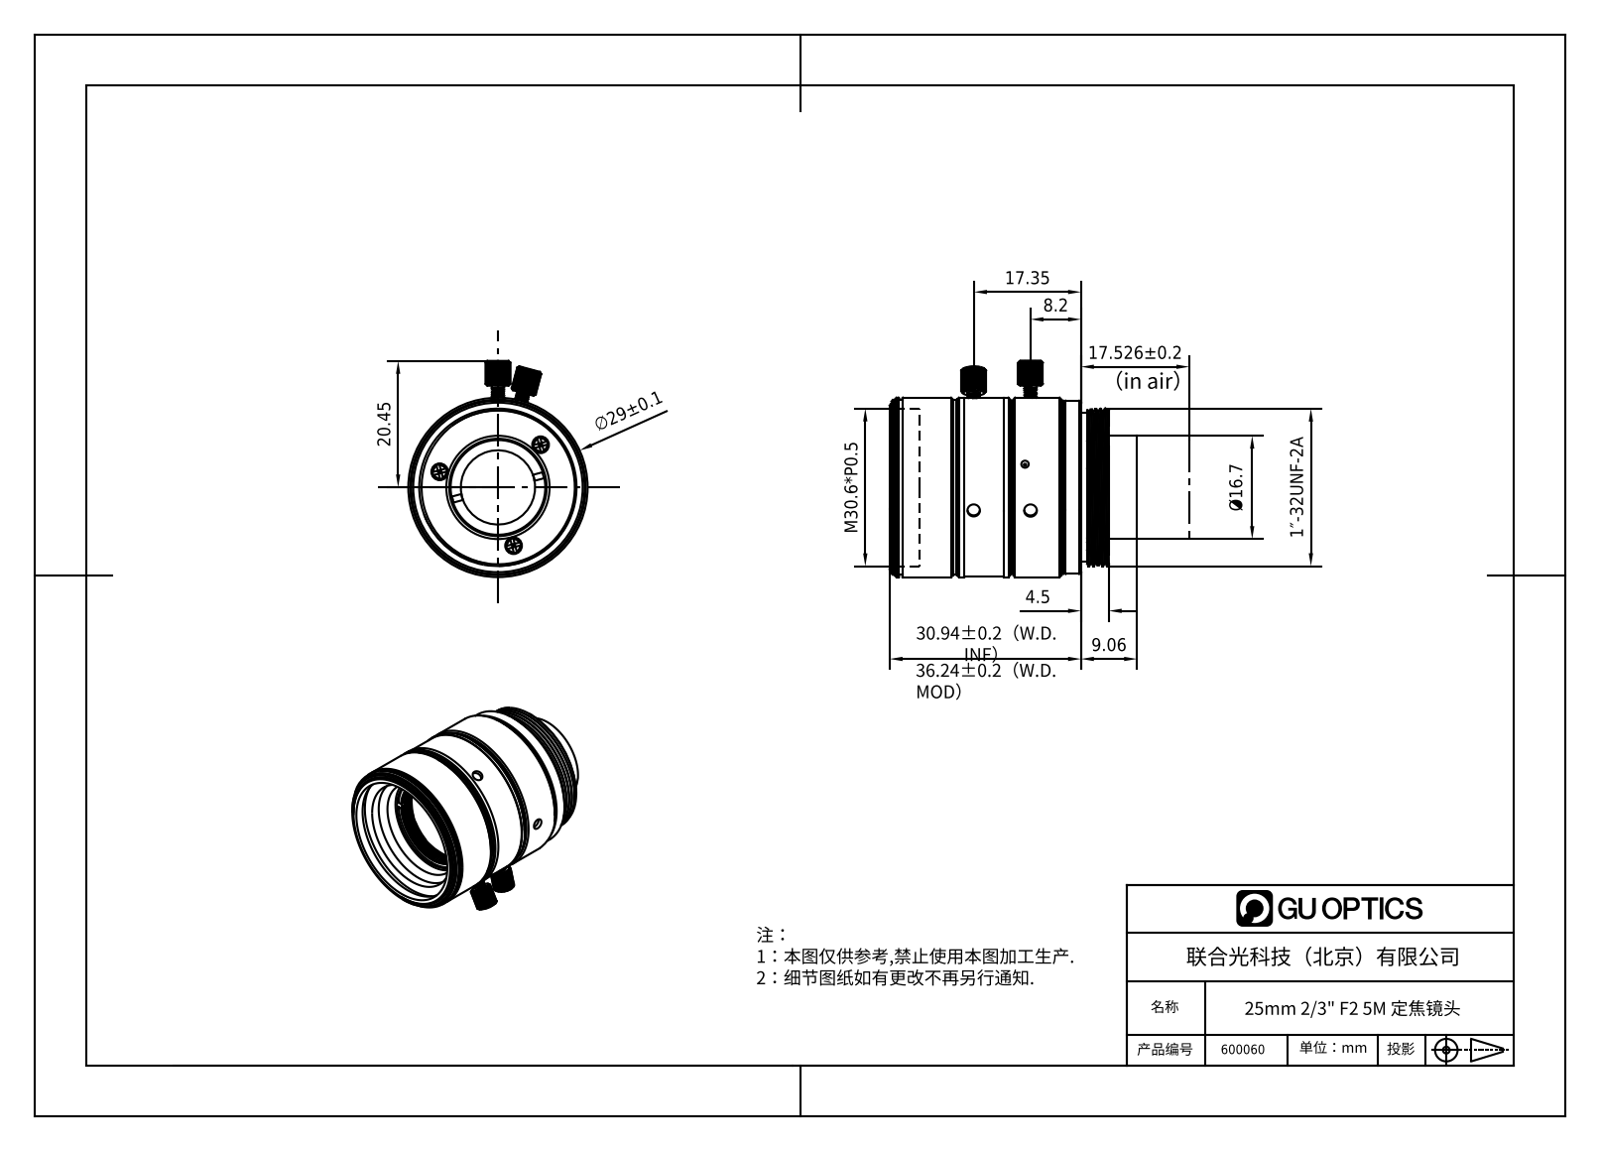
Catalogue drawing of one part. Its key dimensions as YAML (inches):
part_name: "600060"
step_written_by: "SolidWorks 2020 (CONFIG_CONTROL_DESIGN)"
units: inches
bodies: {solids: 8, faces: 821, planar: 263, cylindrical: 396, other: 162}
overall_size: [1.575, 1.366, 1.142]
volume: 1.193
surface_area: 13.84
round_holes:
  - {diameter: 0.065, count: 3}
  - {diameter: 0.079, count: 3}
  - {diameter: 0.106, count: 3}
  - {diameter: 0.081, count: 2}
  - {diameter: 0.472, count: 1}
  - {diameter: 0.539, count: 1}
  - {diameter: 0.596, count: 1}
  - {diameter: 0.633, count: 1}
  - {diameter: 0.641, count: 1}
  - {diameter: 0.648, count: 1}
  - {diameter: 0.656, count: 1}
  - {diameter: 0.657, count: 1}
round_bosses_or_shafts:
  - {diameter: 0.063, count: 6}
  - {diameter: 0.098, count: 3}
  - {diameter: 0.047, count: 3}
  - {diameter: 0.079, count: 2}
  - {diameter: 1.142, count: 1}
  - {diameter: 1.134, count: 1}
  - {diameter: 1.11, count: 1}
  - {diameter: 1.102, count: 1}
partial_cylinders:
  - {radius: 0.133, count: 6}
  - {radius: 0.044, count: 5}
  - {radius: 0.135, count: 4}
  - {radius: 0.044, count: 2}
  - {radius: 0.079, count: 2}
face_to_face_distances: [1.112, 0.12, 1.409, 1.289, 0.298, 0.177, 0.039, 0.032, 0.088, 0.265]
hole_center_spacings: [0.384, 0.665, 0.362, 0.665]
